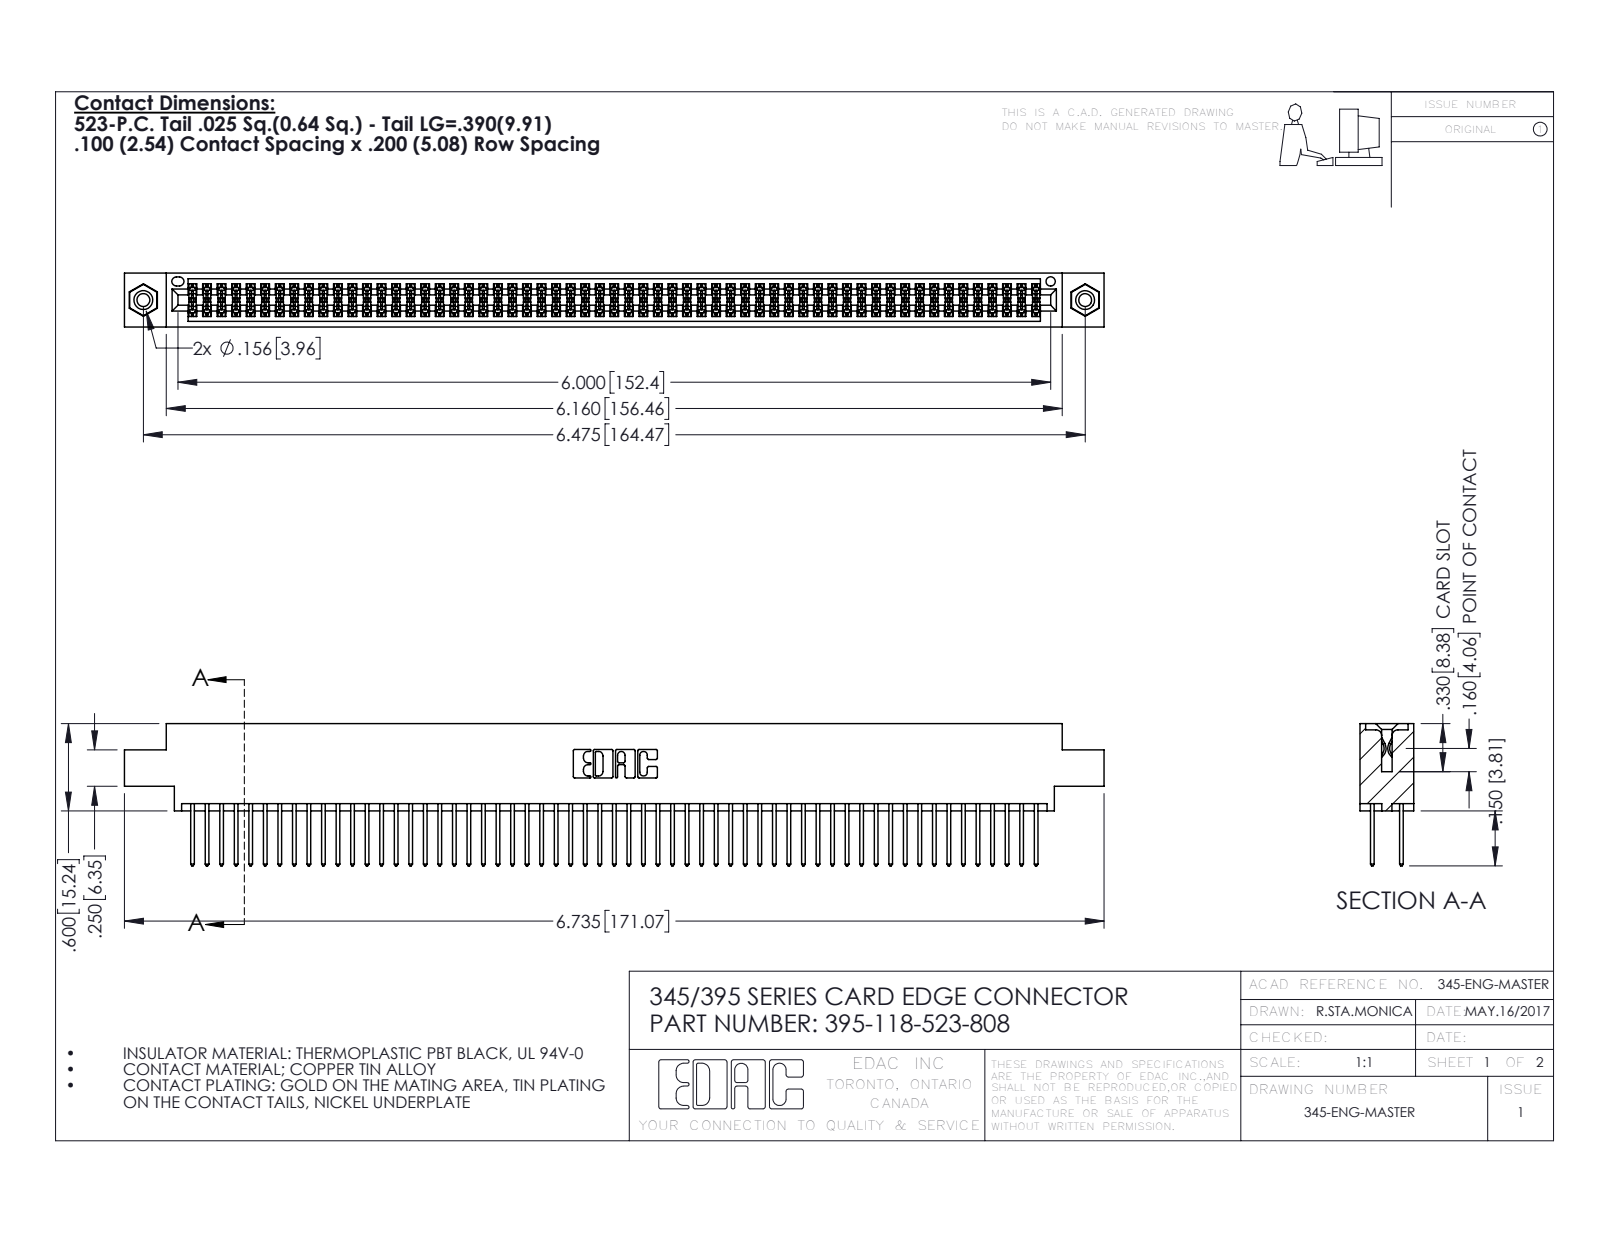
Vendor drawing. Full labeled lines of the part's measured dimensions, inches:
Part name (STEP PRODUCT): 345-250-001_345-250-003-102; 345 Part_0.170 Offset - 0.156 Dia-TI; 395-118-523-808; 345-292-001_345-293-123
STEP written by: SolidWorks 2016 (CONFIG_CONTROL_DESIGN)
Units: inches
Bodies: 121 solids, 6090 faces (4010 planar, 2064 cylindrical, 16 other)
Overall size (bounding box): 6.735 × 0.977 × 0.37
Volume: 1.031 in³ · Surface area: 41.15 in²
Round holes (diameter × count): ⌀0.089 ×2, ⌀0.125 ×2, ⌀0.156 ×2, ⌀0.064 ×1
Round bosses / shafts (diameter × count): ⌀0.155 ×2
Partial cylindrical surfaces — rounded edges, fillets, slot ends (radius × count): R0.006 ×177, R0.01 ×118, R0.01 ×22, R0.007 ×6, R0.031 ×6, R0.026 ×3, R0.014 ×2, R0.019 ×2
Main face-to-face distances: 0.072, 0.298, 0.2, 0.098, 0.272, 0.025, 0.37, 0.225, 0.175, 0.149
Hole centre spacings: 0.27, 6.239, 6.475
